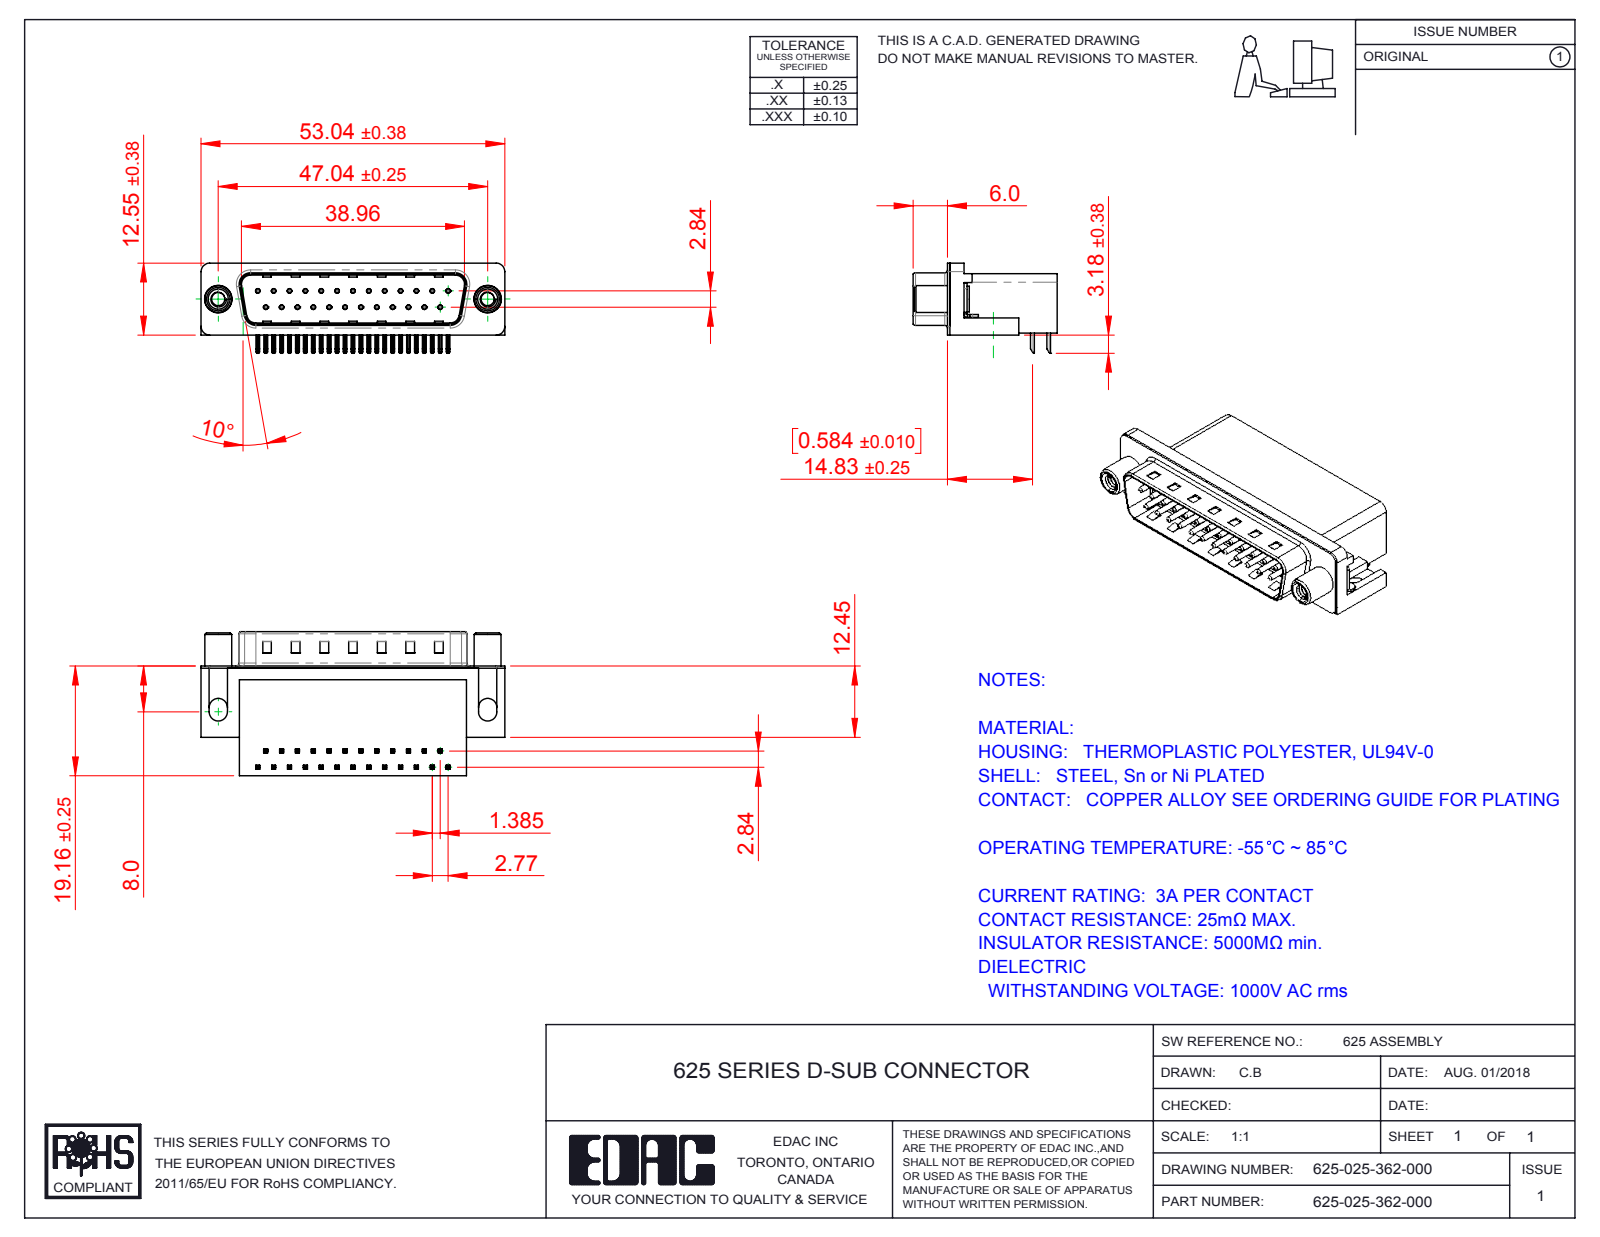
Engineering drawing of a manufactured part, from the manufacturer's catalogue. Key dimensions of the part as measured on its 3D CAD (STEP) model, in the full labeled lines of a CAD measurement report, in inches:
Part name (STEP PRODUCT): 625 Non Board Mount; 625 Shell_25 Socket; 625 Round Threaded Standoff; 625 Housing_25 Socket (+3 more)
STEP written by: SolidWorks 2016 (CONFIG_CONTROL_DESIGN)
Units: inches
Bodies: 31 solids, 2257 faces (1399 planar, 665 cylindrical, 193 other)
Overall size (bounding box): 2.088 × 0.991 × 0.619
Volume: 0.563 in³ · Surface area: 13.84 in²
Round holes (diameter × count): ⌀0.014 ×25, ⌀0.031 ×25, ⌀0.091 ×2, ⌀0.122 ×2, ⌀0.157 ×2, ⌀0.189 ×2, ⌀0.197 ×2
Round bosses / shafts (diameter × count): ⌀0.03 ×25, ⌀0.193 ×2, ⌀0.185 ×2, ⌀0.177 ×2, ⌀0.152 ×2
Partial cylindrical surfaces — rounded edges, fillets, slot ends (radius × count): R0.01 ×100, R0.005 ×50, R0.039 ×16, R0.02 ×9, R0.063 ×8, R0.059 ×7, R0.035 ×4, R0.079 ×4
Main face-to-face distances: 0.016, 0.407, 0.739, 0.083, 0.345, 0.412, 0.428, 0.067, 0.754, 0.114
Hole centre spacings: 0.124, 0.109, 0.436, 0.218, 0.327, 0.198, 0.545, 0.294
